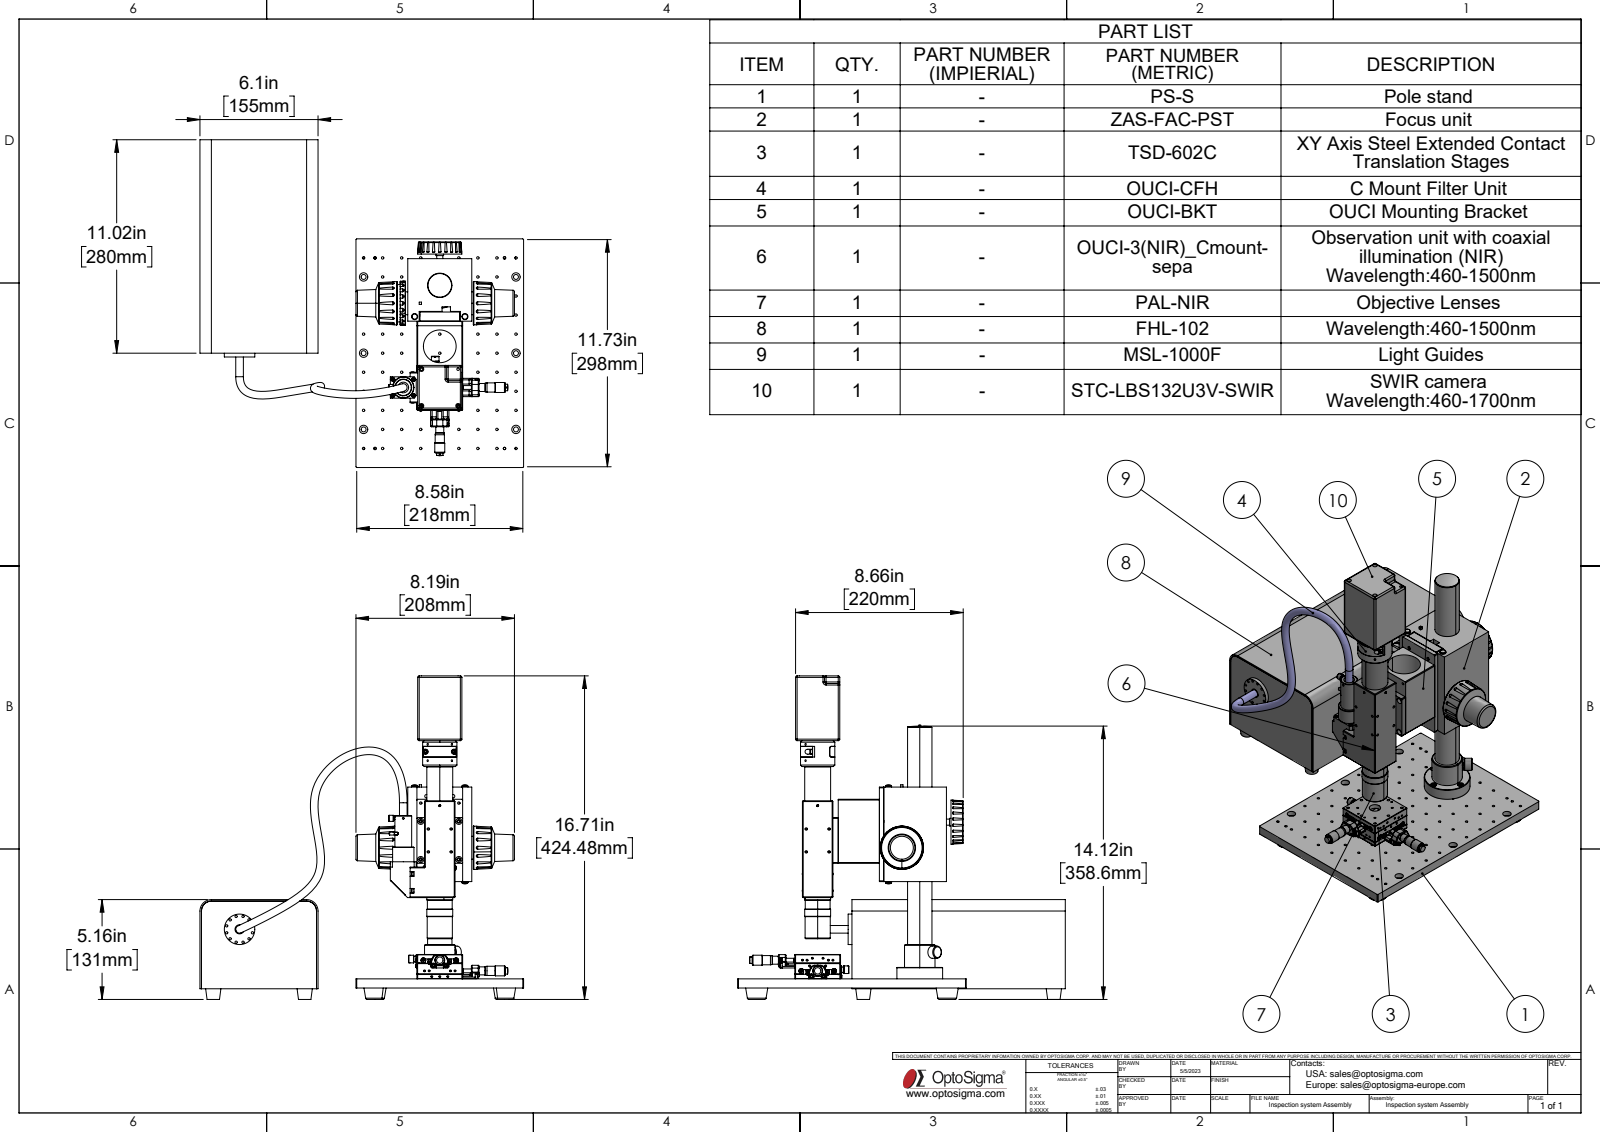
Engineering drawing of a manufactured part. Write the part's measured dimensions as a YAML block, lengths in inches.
part_name: "TSD-602C-C1B-S07.stp; FHL-102; PS-S; TSD-602C (+8 more)"
step_written_by: "SolidWorks 2023 (AUTOMOTIVE_DESIGN)"
units: inches
bodies: {solids: 38, faces: 4013, planar: 1424, cylindrical: 1395, other: 1194}
overall_size: [18.05, 16.929, 16.724]
volume: 489.1
surface_area: 1542
round_holes:
  - {diameter: 0.126, count: 118}
  - {diameter: 0.315, count: 21}
  - {diameter: 0.118, count: 16}
  - {diameter: 0.177, count: 16}
  - {diameter: 0.197, count: 14}
  - {diameter: 0.102, count: 12}
  - {diameter: 0.236, count: 9}
  - {diameter: 0.079, count: 8}
  - {diameter: 0.094, count: 7}
  - {diameter: 0.256, count: 7}
  - {diameter: 0.433, count: 6}
  - {diameter: 0.098, count: 5}
round_bosses_or_shafts:
  - {diameter: 0.276, count: 18}
  - {diameter: 0.217, count: 14}
  - {diameter: 0.157, count: 14}
  - {diameter: 0.177, count: 12}
  - {diameter: 0.118, count: 12}
  - {diameter: 0.236, count: 9}
  - {diameter: 0.079, count: 8}
  - {diameter: 0.094, count: 6}
partial_cylinders:
  - {radius: 0.012, count: 64}
  - {radius: 0.079, count: 43}
  - {radius: 0.098, count: 36}
  - {radius: 0.039, count: 32}
  - {radius: 0.071, count: 22}
  - {radius: 0.128, count: 14}
  - {radius: 0.118, count: 12}
  - {radius: 0.094, count: 4}
face_to_face_distances: [0.079, 0.472, 4.488, 4.016, 5.945, 6.024, 0.039, 0.512, 4.528, 4.567]
hole_center_spacings: [2.201, 0.984, 1.969, 1.392, 3.113, 3.549, 2.784, 2.953]
